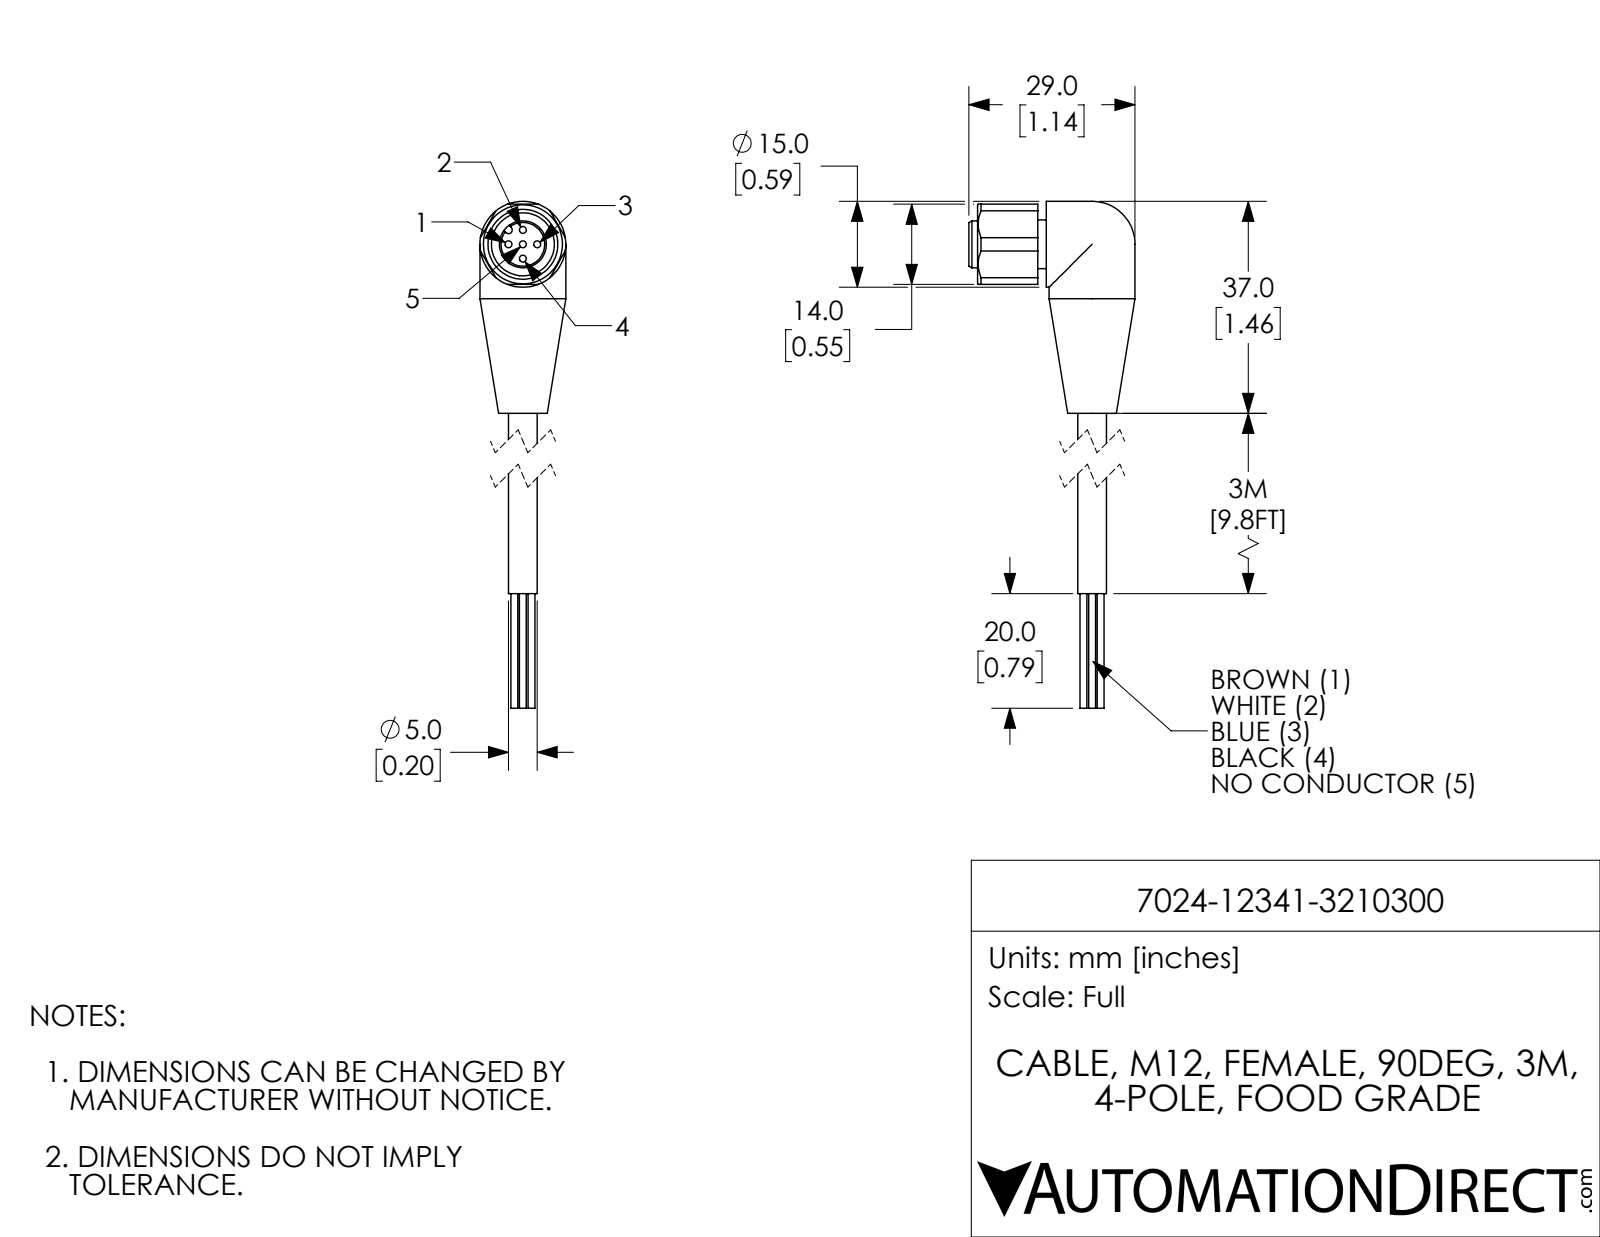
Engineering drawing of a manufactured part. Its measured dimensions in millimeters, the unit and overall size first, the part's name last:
Units: millimetres
Overall size (bounding box): 87 × 29 × 15
Round holes (diameter × count): ⌀1.2 ×5, ⌀11 ×1
Round bosses / shafts (diameter × count): ⌀1.2 ×4, ⌀15 ×2, ⌀8.5 ×1, ⌀8.2 ×1, ⌀5 ×1
Partial cylindrical surfaces — rounded edges, fillets, slot ends (radius × count): R0.65 ×1
Main face-to-face distances: 14, 1.5, 12, 4.5, 3, 13.5, 9, 22.5, 36.5, 10.5
Hole centre spacings: 2.5, 3.54, 5
Volume: 7 402 mm³ · Surface area: 3 886 mm²
Bodies: 1 solid, 73 faces (25 planar, 38 cylindrical, 10 other)
Part name (STEP PRODUCT): 7024-12341-3210300
STEP written by: SolidWorks 2018 (AUTOMOTIVE_DESIGN)
